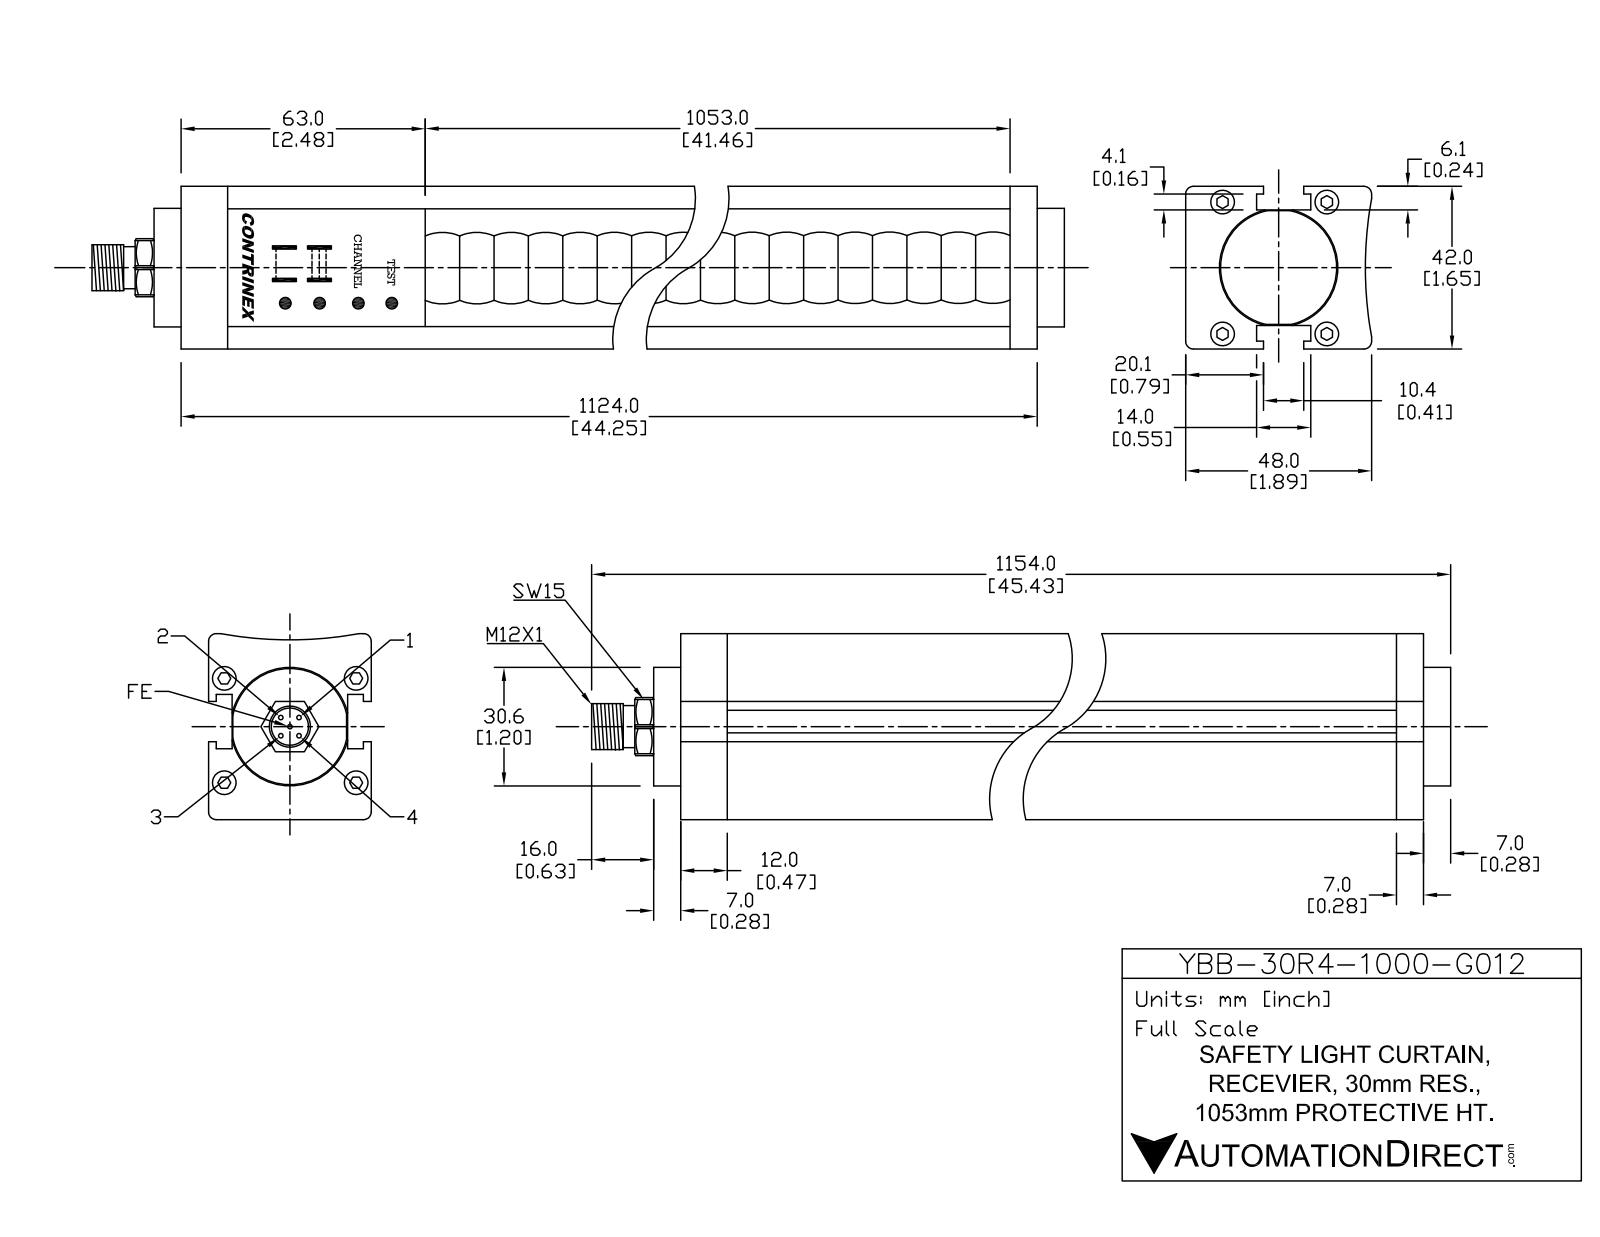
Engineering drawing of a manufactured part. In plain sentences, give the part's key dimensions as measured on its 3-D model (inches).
The part is named "YBB-30R4-1000-G012". Its 3-D file was written by "SolidWorks 2016 (AUTOMOTIVE_DESIGN)". It is 19 solids with 440 faces: 208 planar, 168 cylindrical and 64 other. Overall it measures 45.433 by 1.89 by 1.654 inches. Its volume is 123.4 cubic inches and its surface area 398.9 square inches. Round holes: 4 of diameter 0.236, 1 of diameter 0.335, 1 of diameter 1.26. Round bosses or shafts: 5 of diameter 0.039, 4 of diameter 0.217, 1 of diameter 1.205, 1 of diameter 0.472, 1 of diameter 0.413. Partial cylindrical surfaces (rounded edges, fillets, slot ends): 48 of radius 0.039, 4 of radius 0.02, 2 of radius 0.022, 1 of radius 0.323, 1 of radius 3.937. The main face-to-face distances are 0.248, 1.406, 1.654, 1.157, 0.551, 0.677, 1.228, 0.618, 1.169, 1.846. The hole center spacings are 0.828, 0.88, 1.059, 1.339, 1.707.
